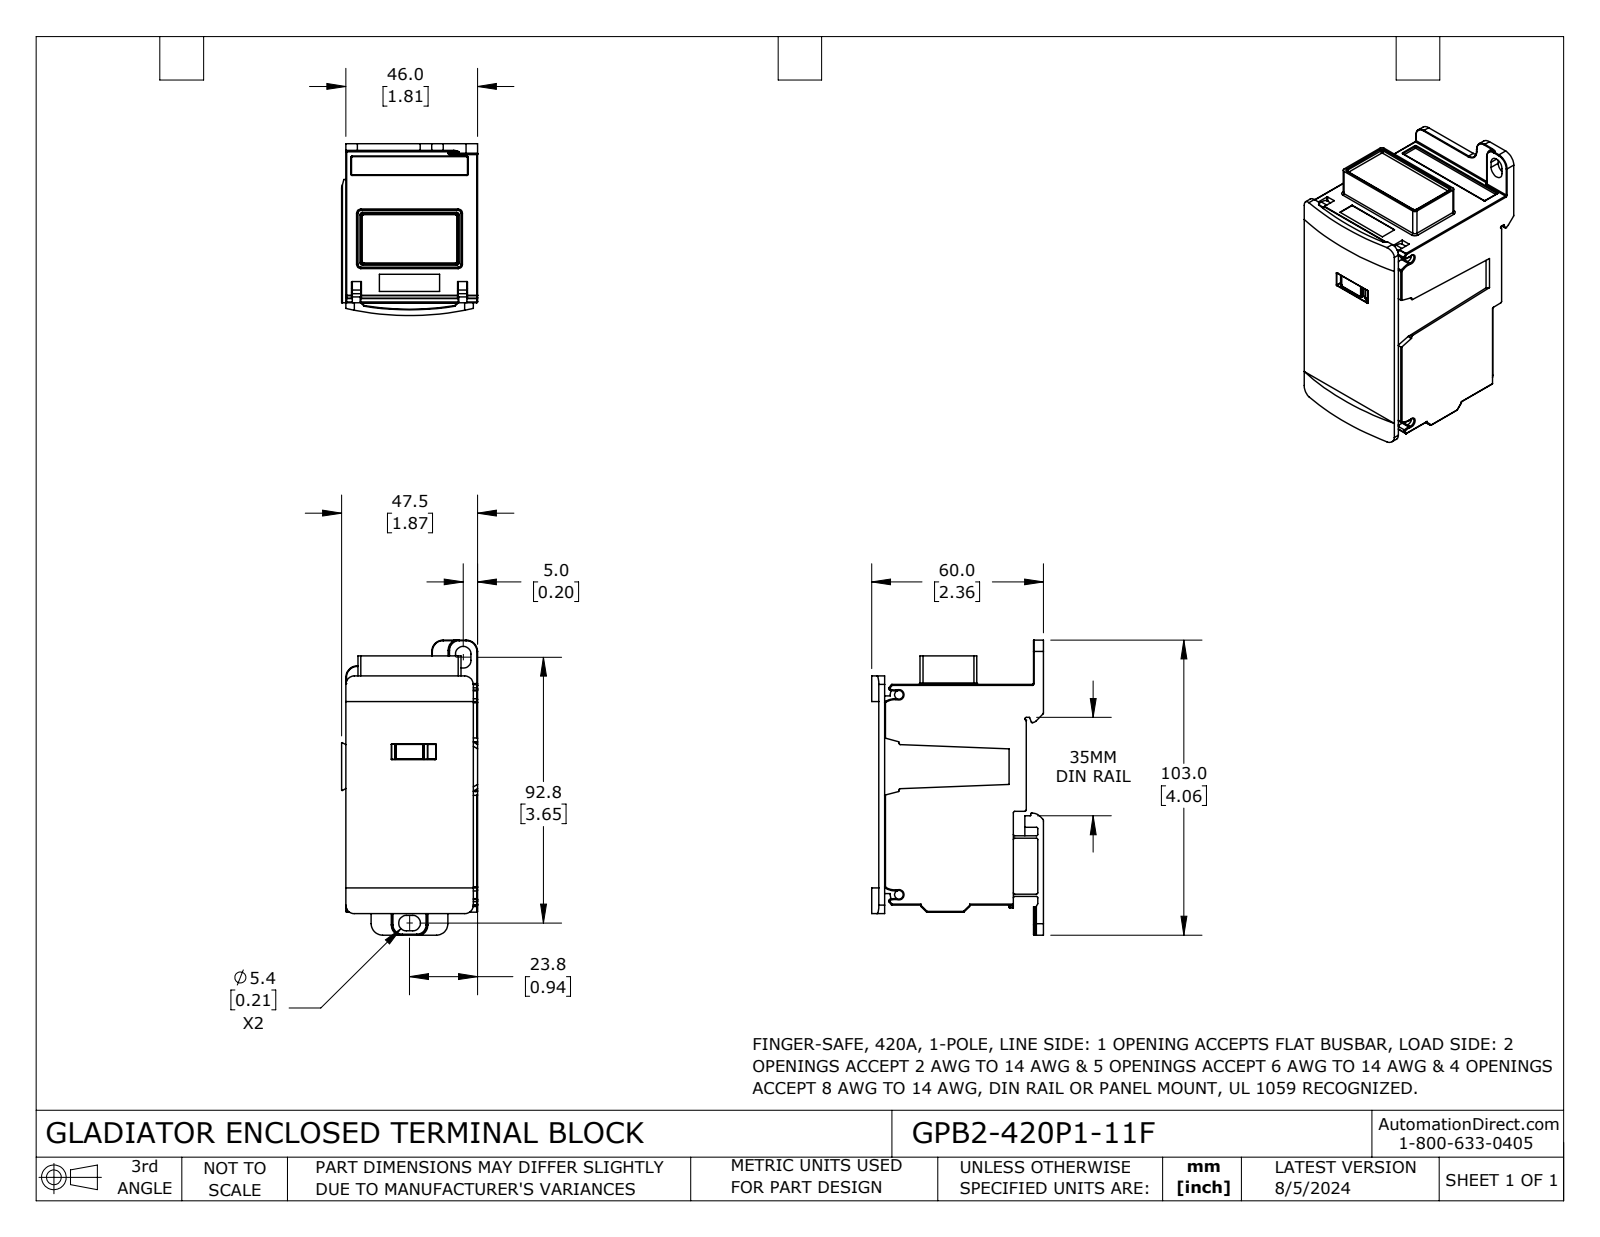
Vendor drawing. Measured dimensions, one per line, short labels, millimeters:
name: GPB2-420P1-11F
written by: SolidWorks 2023 (CONFIG_CONTROL_DESIGN)
unit: mm
bodies: 1 solid, 611 faces (226 planar, 280 cylindrical, 105 other)
size: 103 × 60 × 47.5
volume: 191 200 mm³; area: 28 570 mm²
holes: 5× ⌀10, 4× ⌀8.5, 2× ⌀3, 2× ⌀12.3
rounds: 50× R0.2, 32× R0.5, 30× R0.3, 25× R0.1, 7× R4, 6× R3, 5× R1, 4× R2.7
face distances: 46, 1, 57.5, 6, 51.5, 2, 76, 4.5, 77, 10.5
hole spacings: 9.5, 10.5, 14.1, 21.5, 23.5, 11, 11.5, 12.3
